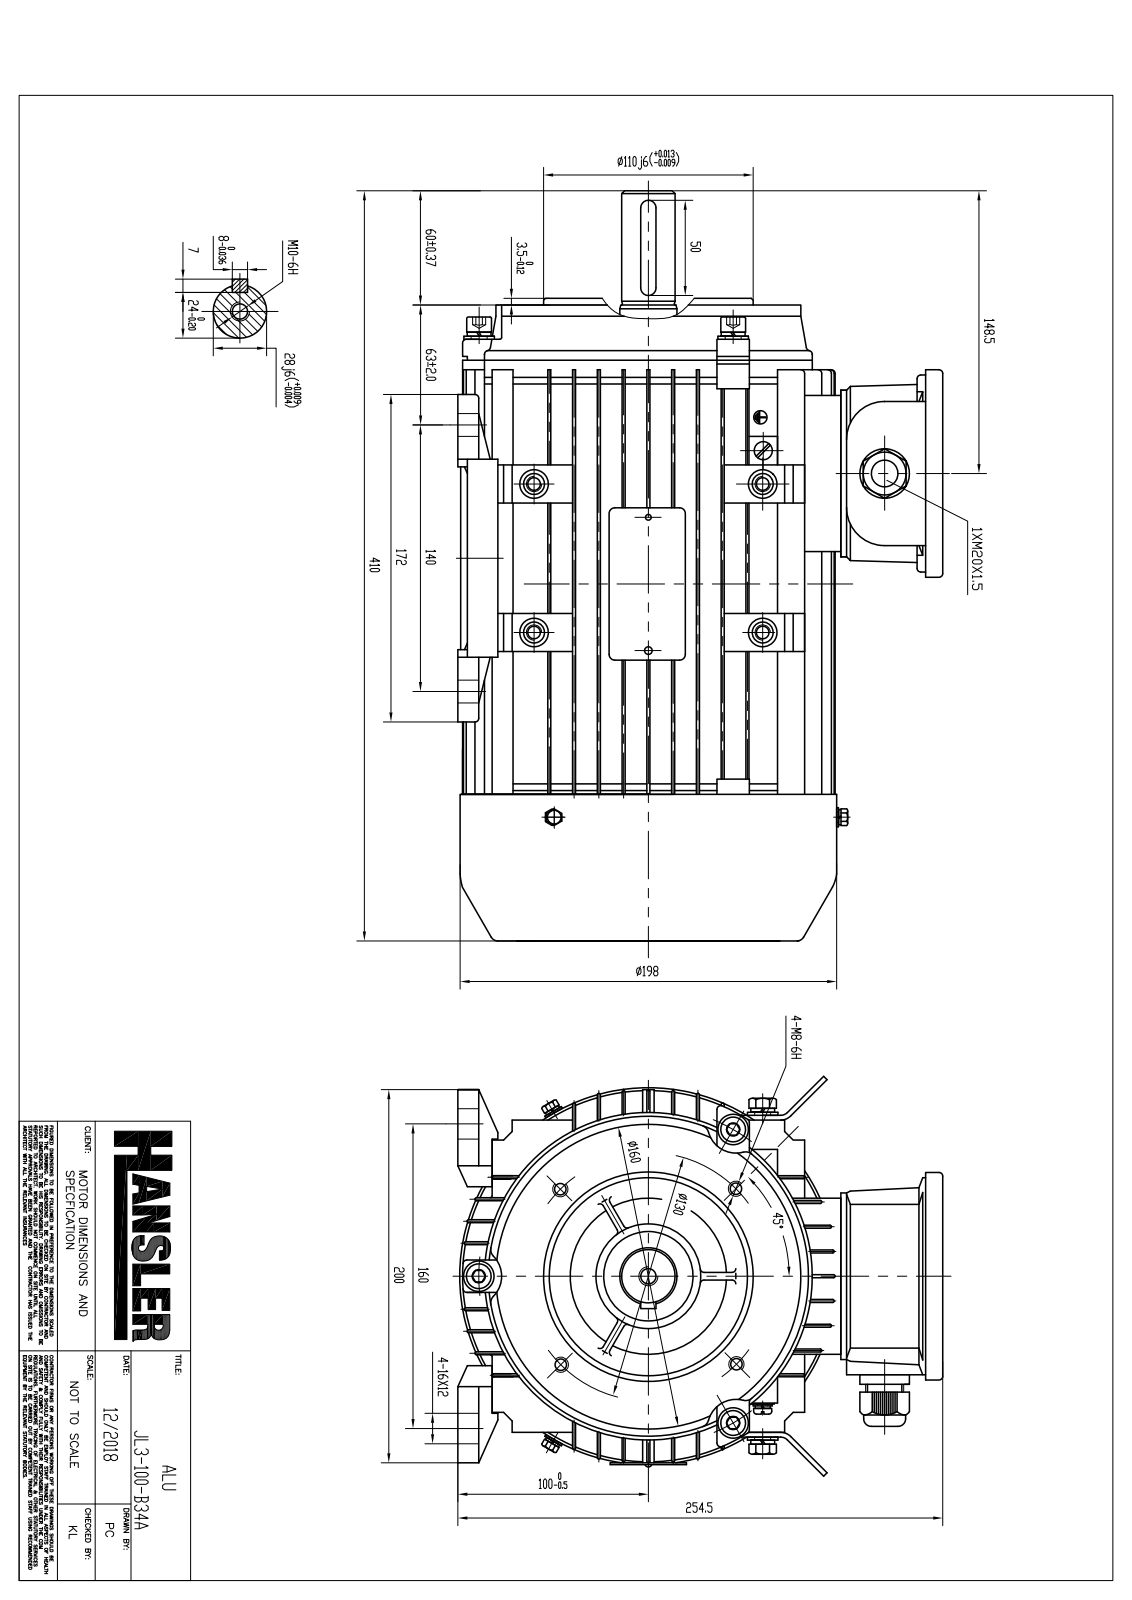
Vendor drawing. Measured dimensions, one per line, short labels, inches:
name: JL3-100-B34A
written by: SolidWorks 2018 (CONFIG_CONTROL_DESIGN)
unit: in
bodies: 53 solids, 4426 faces (1875 planar, 1716 cylindrical, 835 other)
size: 15.63 × 10.135 × 8.268
volume: 109.4 in³; area: 1 643 in²
holes: 14× ⌀0.228, 11× ⌀0.276, 8× ⌀0.63, 7× ⌀0.354, 6× ⌀0.157, 5× ⌀0.315, 4× ⌀0.197, 4× ⌀0.394, 4× ⌀0.472, 3× ⌀0.207, 3× ⌀0.209, 3× ⌀0.33
bosses: 11× ⌀0.591, 9× ⌀0.315, 8× ⌀0.433, 7× ⌀0.197, 4× ⌀0.512, 4× ⌀0.354, 3× ⌀0.496, 3× ⌀0.394
rounds: 544× R0.02, 121× R0.039, 52× R0.079, 34× R0.157, 31× R0.118, 20× R0.236, 16× R0.012, 12× R0.013
face distances: 0.512, 1.024, 1.535, 2.047, 0.063, 0.575, 0.449, 2.559, 1.087, 0.961
hole spacings: 2.362, 3.034, 3.583, 0.042, 0.591, 0.71, 0.803, 0.863
